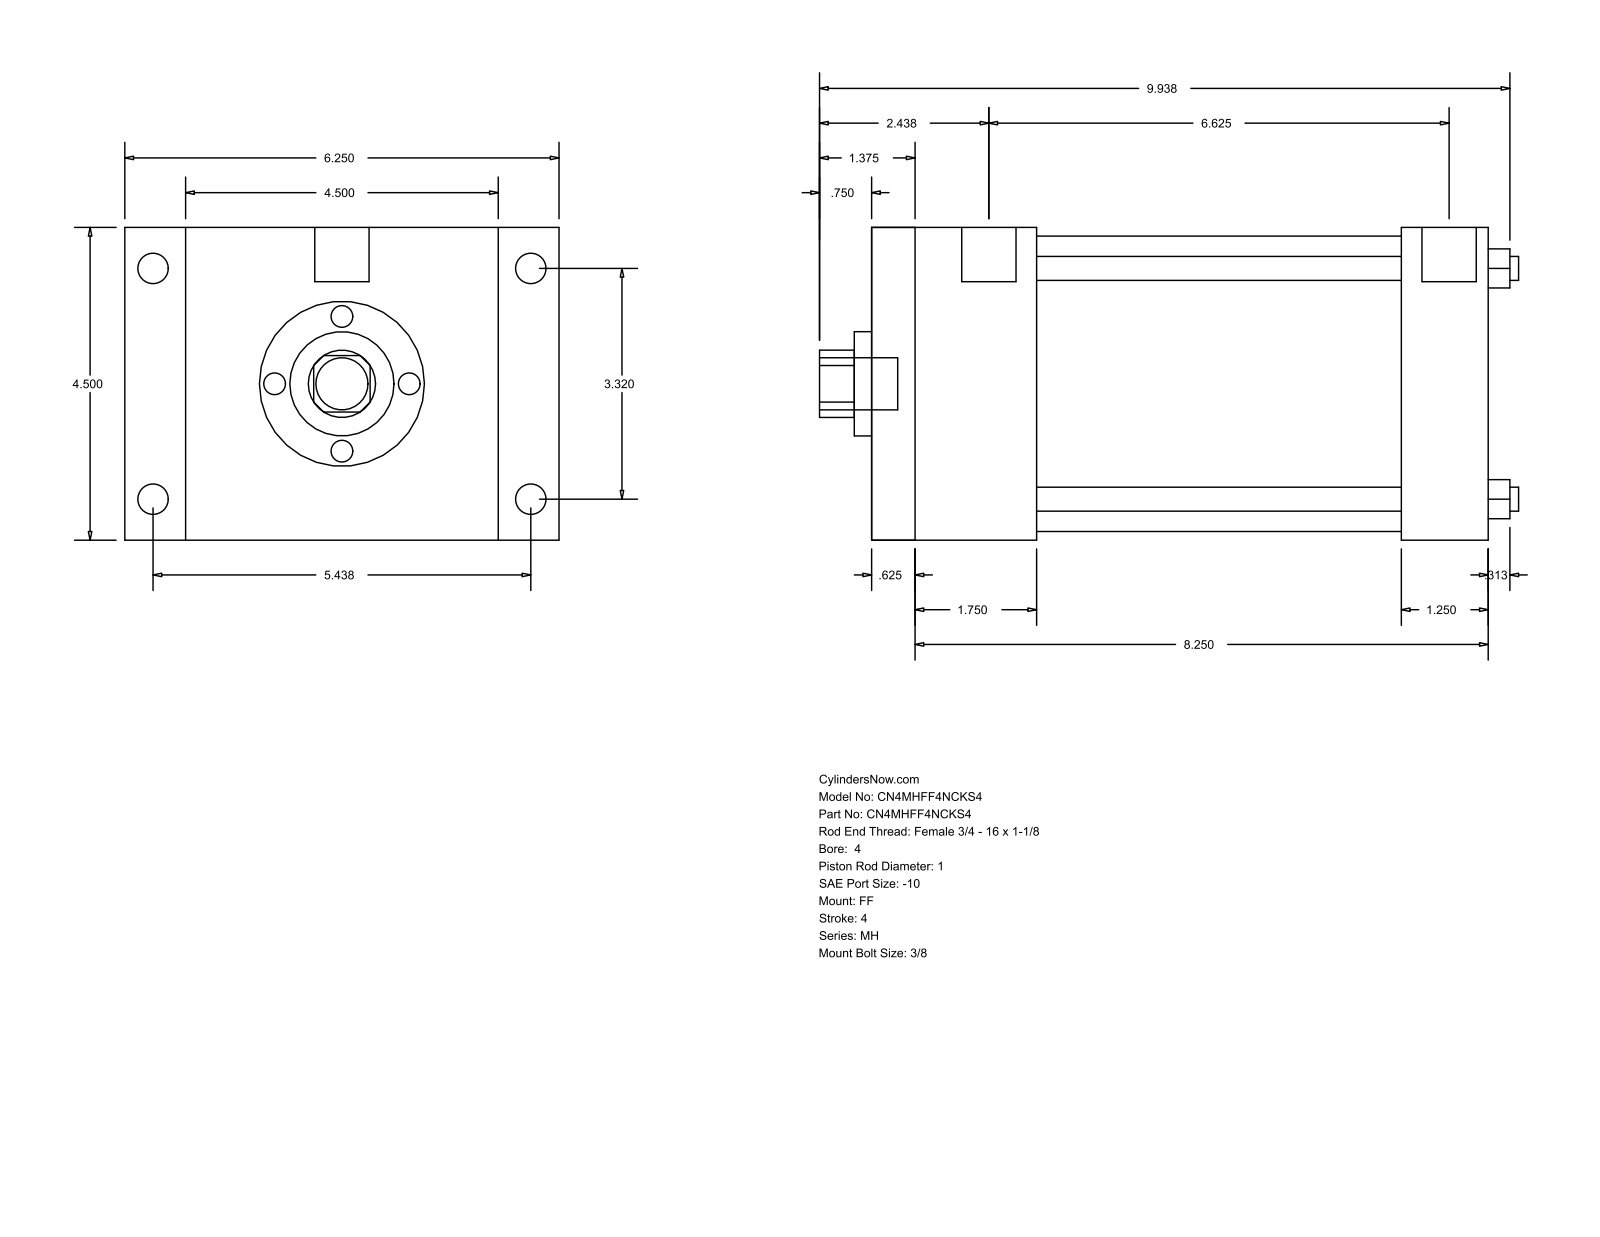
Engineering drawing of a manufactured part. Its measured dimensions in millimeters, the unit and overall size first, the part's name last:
Units: millimetres
Overall size (bounding box): 255.59 × 158.75 × 114.3
Round holes (diameter × count): ⌀8.76 ×4, ⌀25.4 ×1, ⌀38.1 ×1, ⌀107.95 ×1
Round bosses / shafts (diameter × count): ⌀11.13 ×4, ⌀8.73 ×4, ⌀19.84 ×2, ⌀19.05 ×1
Partial cylindrical surfaces — rounded edges, fillets, slot ends (radius × count): R12.29 ×1
Main face-to-face distances: 114.3, 225.42, 15.87, 209.55, 60.33, 44.46, 165.09, 193.67, 177.8, 133.34
Hole centre spacings: 59.62, 84.32, 119.25
Bodies: 0 solids, 92 faces (64 planar, 28 cylindrical, 0 other)
Part name (STEP PRODUCT): MH_FF__0400_1
STEP written by: GSSL Pune (CONFIG_CONTROL_DESIGN)
